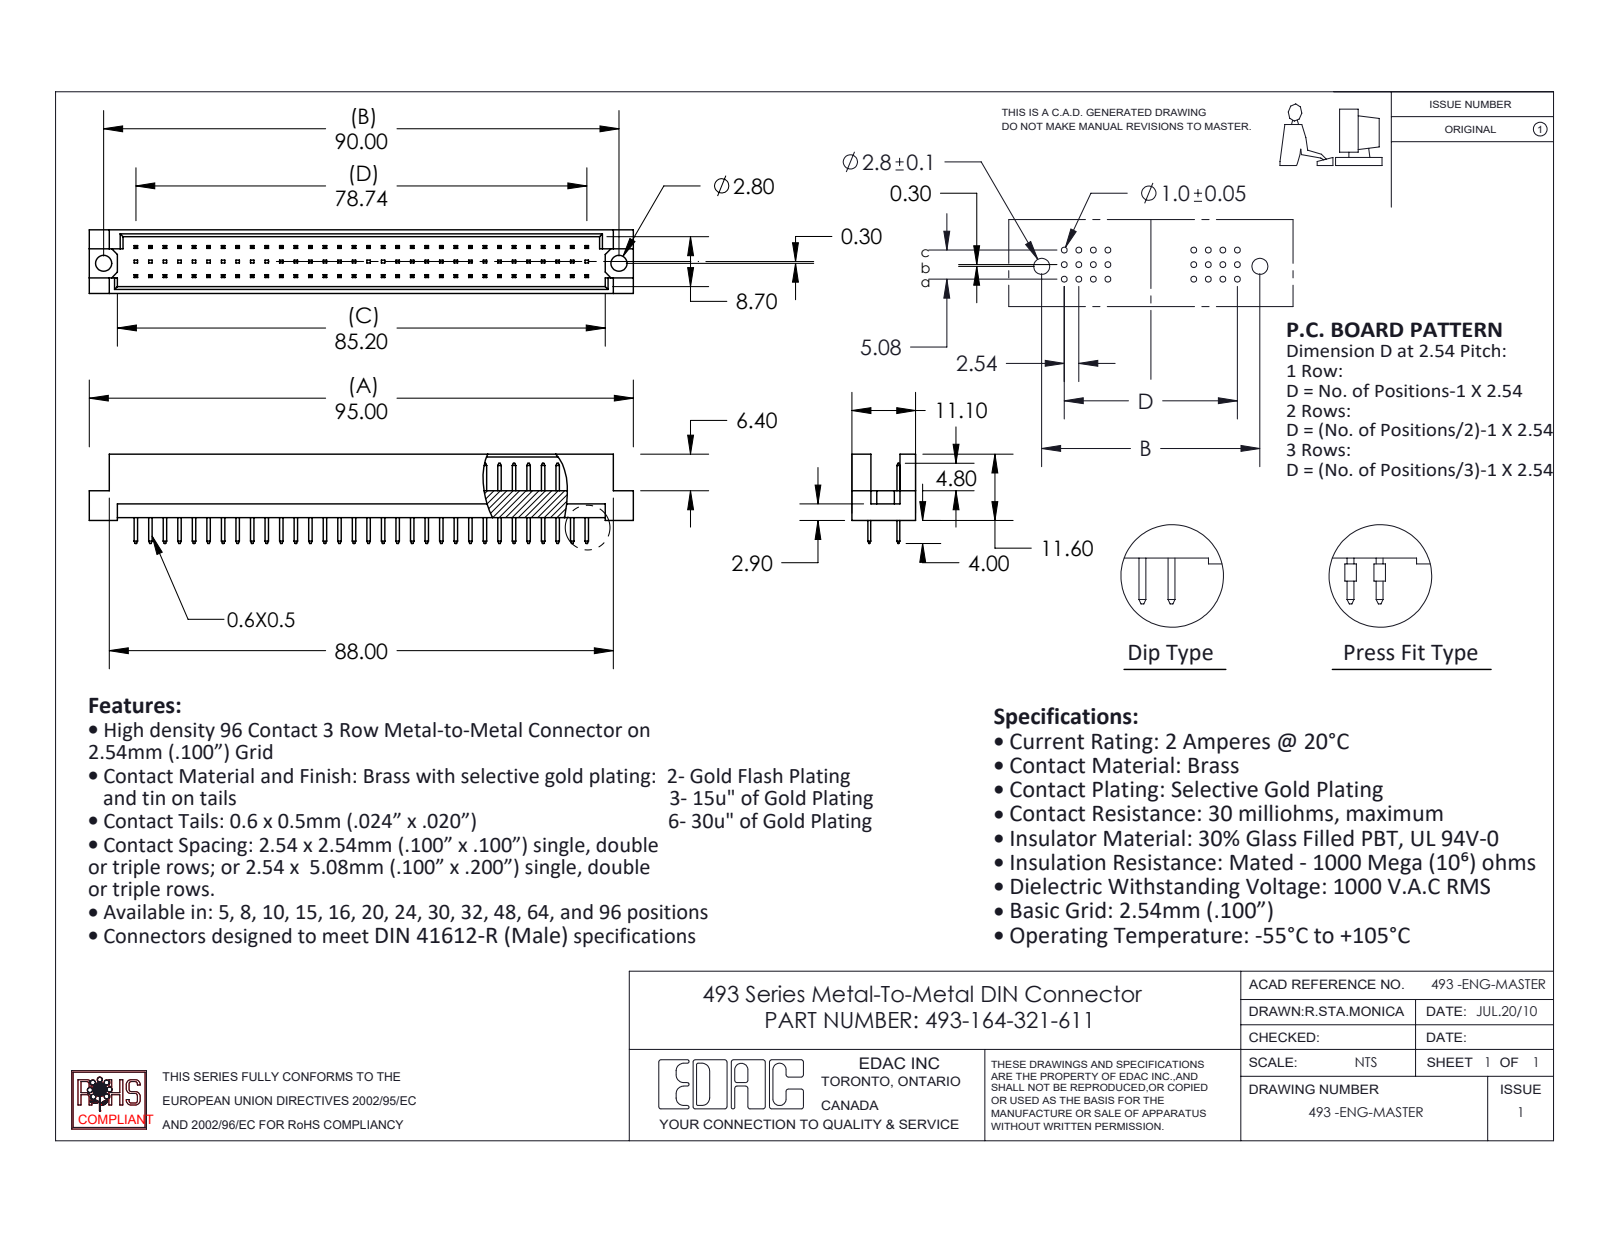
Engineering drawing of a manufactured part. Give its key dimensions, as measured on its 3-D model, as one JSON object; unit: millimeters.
{"part_name": "493 Part_96; 493-290_21; 493-164-321-611", "step_written_by": "SolidWorks 2020 (CONFIG_CONTROL_DESIGN)", "units": "millimeters", "bodies": {"solids": 65, "faces": 1332, "planar": 1328, "cylindrical": 4, "other": 0}, "overall_size": [95, 15.6, 11.1], "volume_mm3": 5920, "surface_area_mm2": 8421, "round_holes": [[2.8, 2]], "face_to_face_distances": [1.2, 9.9, 5.08, 11.1, 0.5, 8.7, 4.7, 2.76, 3.26, 7.84], "hole_center_spacings": [90]}
